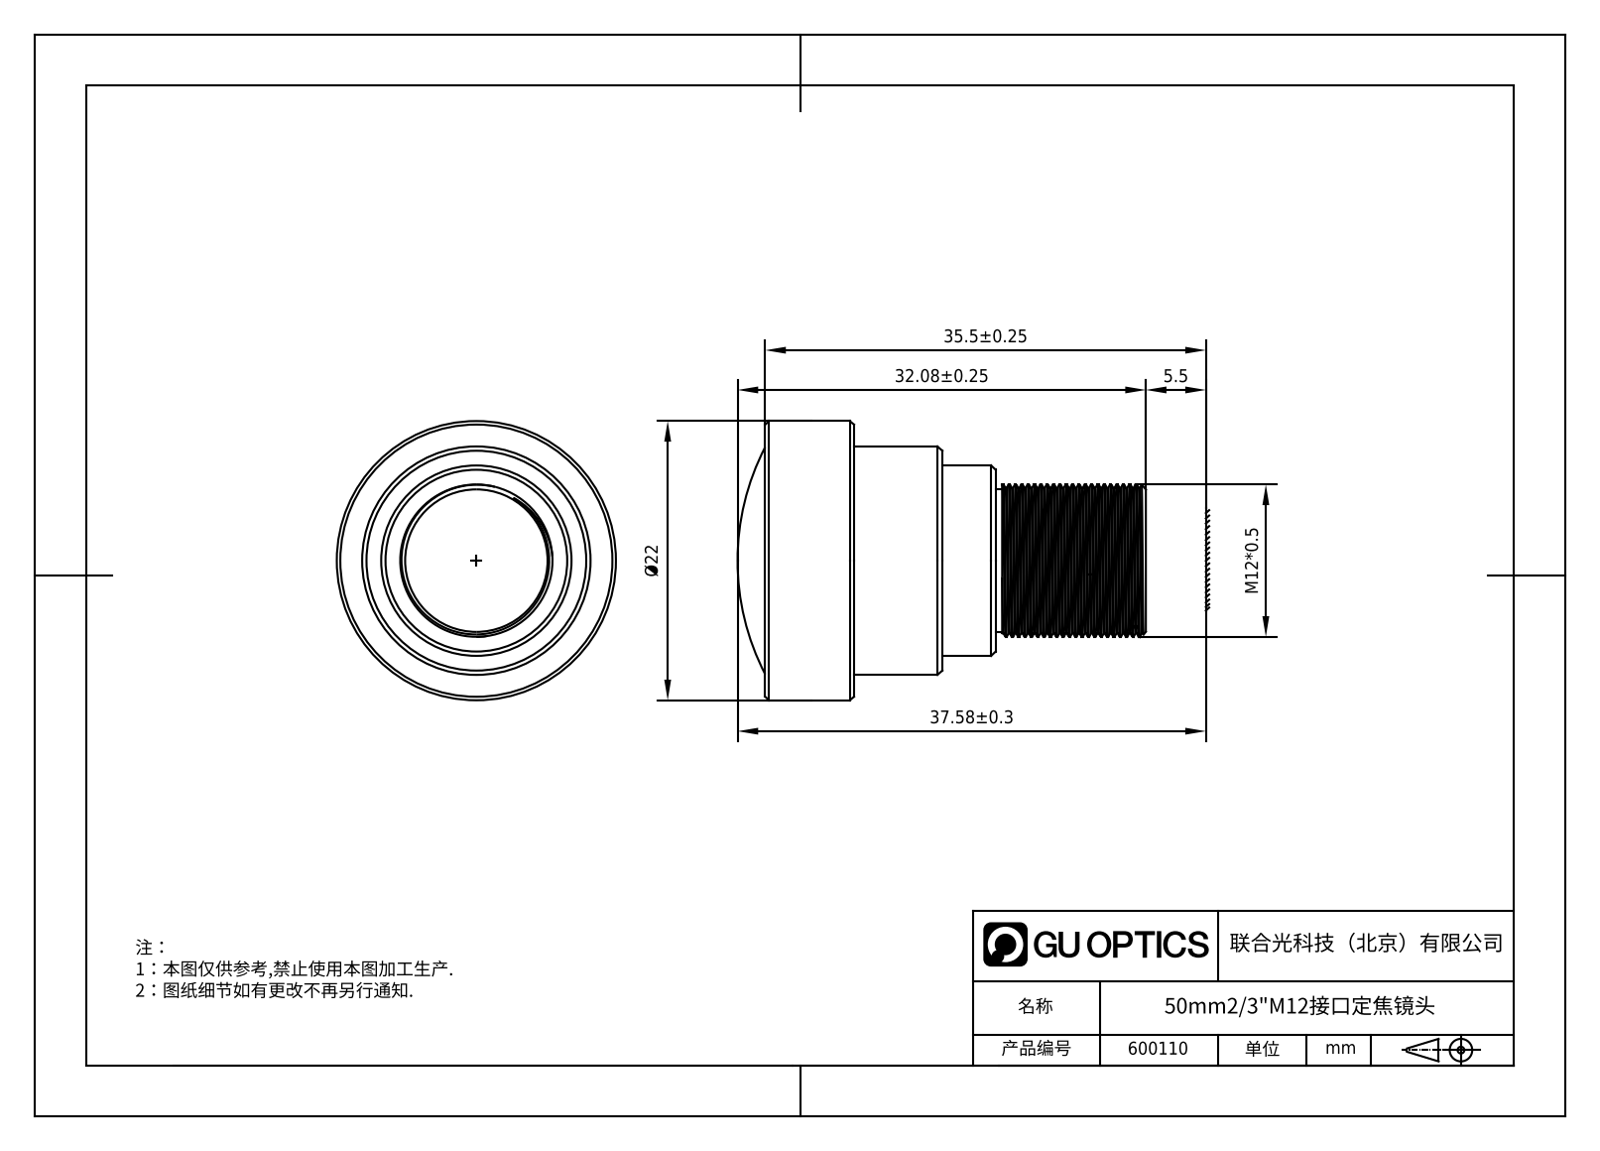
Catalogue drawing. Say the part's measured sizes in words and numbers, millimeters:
The part is named "600110". Its 3-D file was written by "SolidWorks 2020 (CONFIG_CONTROL_DESIGN)". It is 1 solid with 38 faces: 6 planar, 5 cylindrical and 27 other. Overall it measures 32.08 by 22 by 22 millimeters. Its volume is 6 717 cubic millimeters and its surface area 2 527 square millimeters. Round bosses or shafts: 1 of diameter 22, 1 of diameter 18, 1 of diameter 15, 1 of diameter 12, 1 of diameter 11. The main face-to-face distances are 7, 11.5, 30, 23, 18.5, 14, 4.5, 16, 19, 12.
